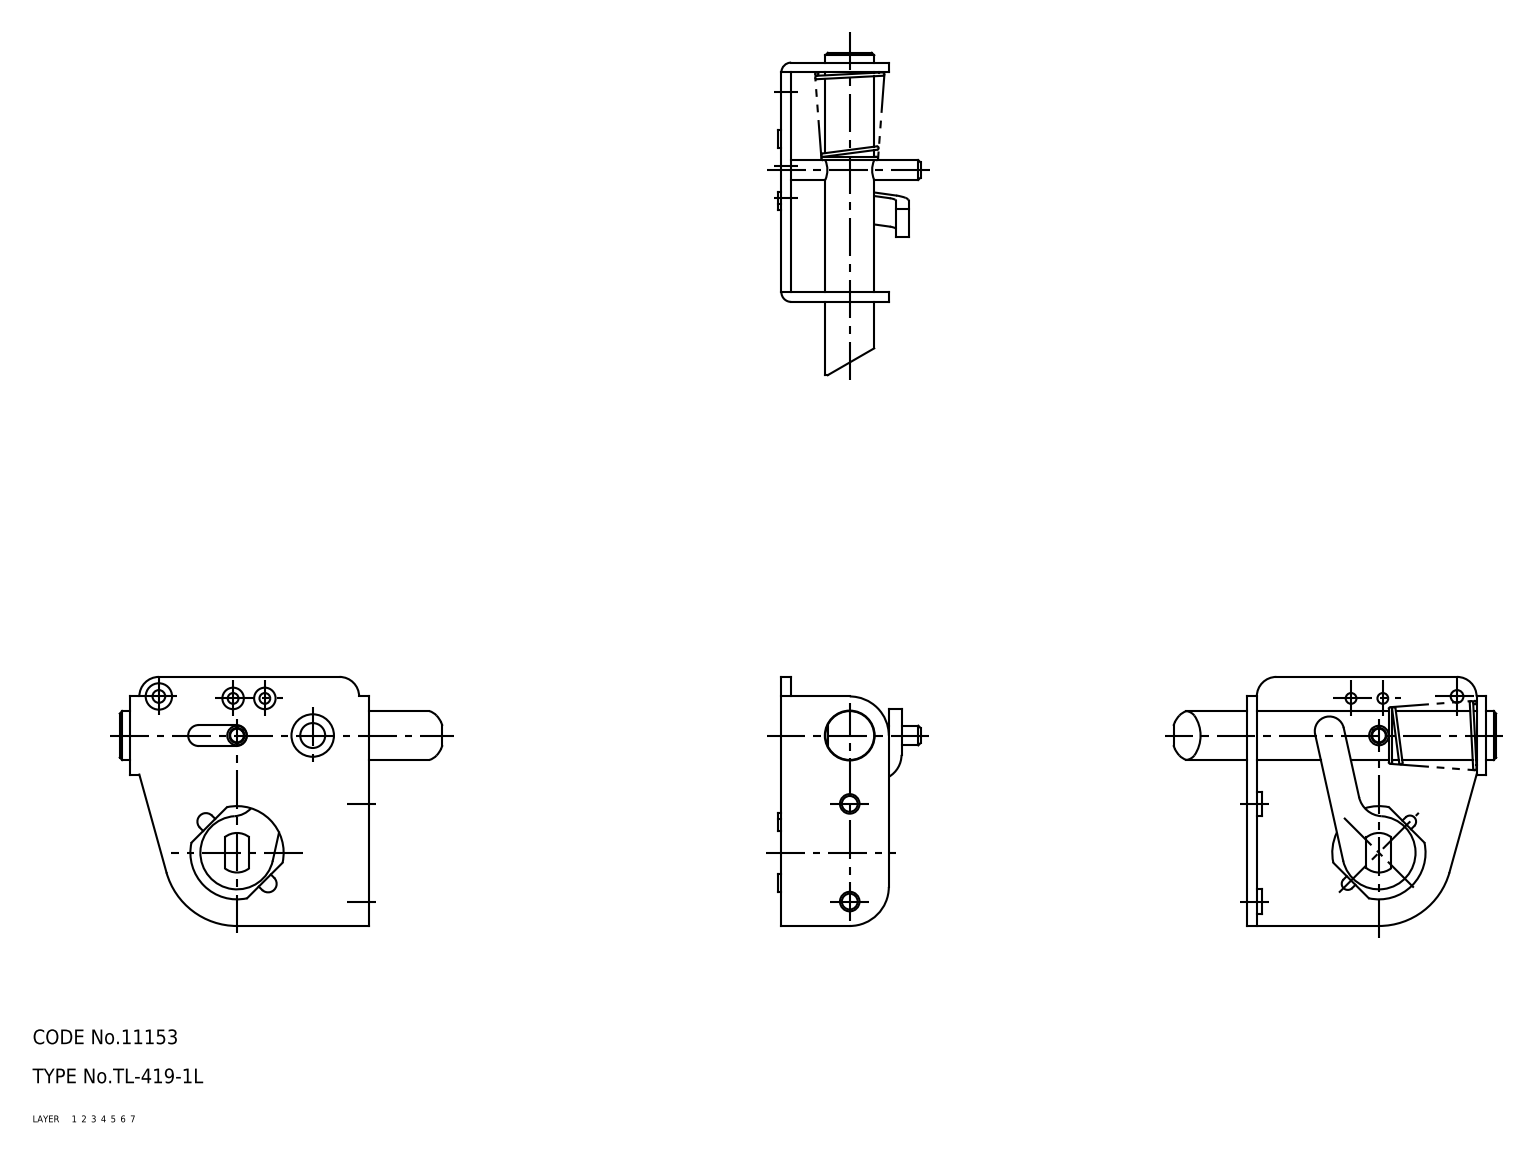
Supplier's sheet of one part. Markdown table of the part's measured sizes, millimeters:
| quantity | value |
| --- | --- |
| part name | TL-419-1L組立; カム_mr-1; TL_419_1L |
| STEP written by | SolidWorks 2015 (AUTOMOTIVE_DESIGN) |
| units | millimeters |
| bodies | 2 solids, 166 faces (50 planar, 84 cylindrical, 32 other) |
| overall size | 66 × 51 × 29.2 |
| volume | 11 763 mm³ |
| surface area | 11 224 mm² |
| round holes (diameter × count) | 2.2 × 2, 3.25 × 2, 2.6 × 1, 2.8 × 1, 5.1 × 1, 10.2 × 1 |
| round bosses / shafts (diameter × count) | 5 × 2, 14.2 × 1, 10 × 1, 4 × 1 |
| partial cylindrical surfaces (radius × count) | 2 × 3, 0.3 × 2, 1.25 × 2, 1.75 × 2, 2.15 × 2, 2.6 × 2, 4 × 2, 5.2 × 2 |
| main face-to-face distances | 2, 47, 49, 2.6, 45, 15, 13, 17.6, 15.6, 7 |
| hole center spacings | 6.5, 7.63, 9.59, 12.4, 14, 15.21, 15.65, 17.75 |
